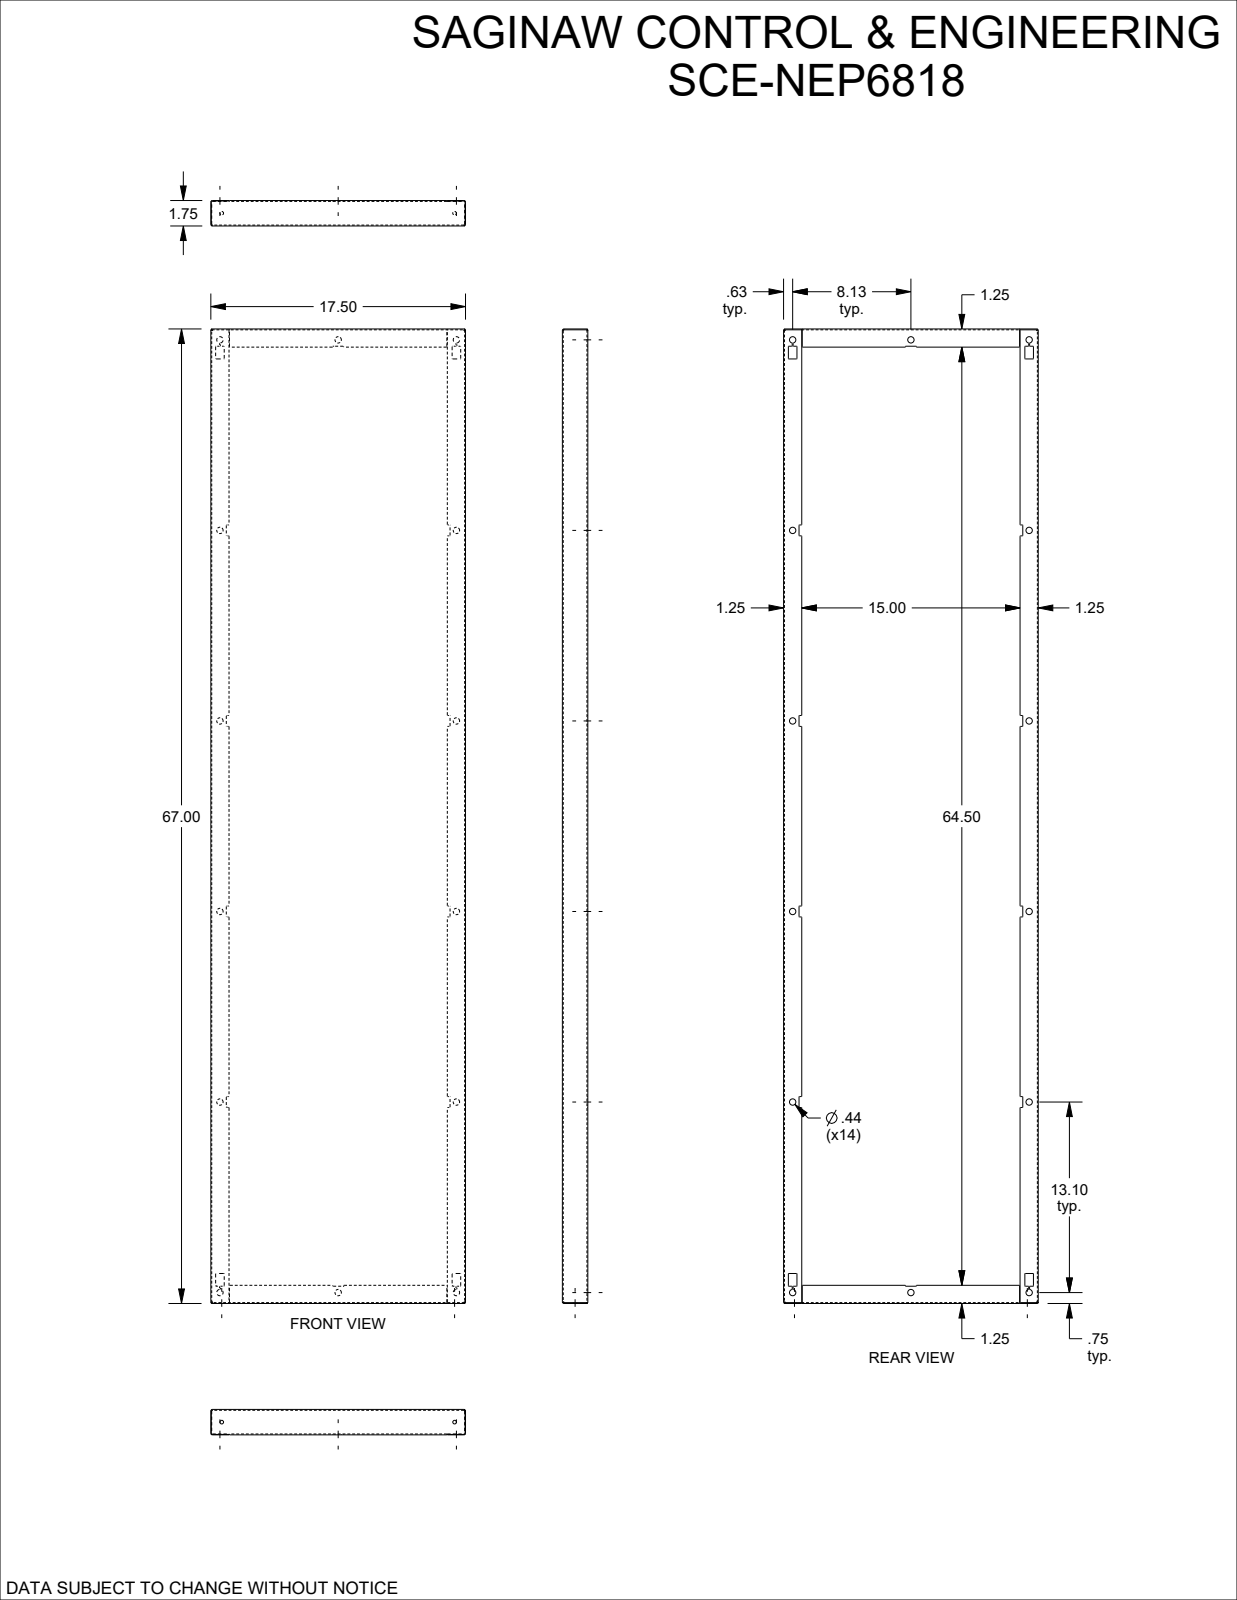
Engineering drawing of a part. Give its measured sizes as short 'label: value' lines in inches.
name: SCE-NEP6818
written by: SolidWorks 2023 (AUTOMOTIVE_DESIGN)
unit: in
bodies: 1 solid, 170 faces (84 planar, 86 cylindrical, 0 other)
size: 67 × 17.5 × 1.75
volume: 98.57 in³; area: 3 306 in²
holes: 14× ⌀0.437
rounds: 72× R0.03
face distances: 0.06, 1.69, 17.44, 1.75, 1.63, 17.5, 17.38, 66.94, 67, 66.88
hole spacings: 13.1, 20.873, 26.2, 30.83, 16.25, 39.3, 42.527, 8.125
